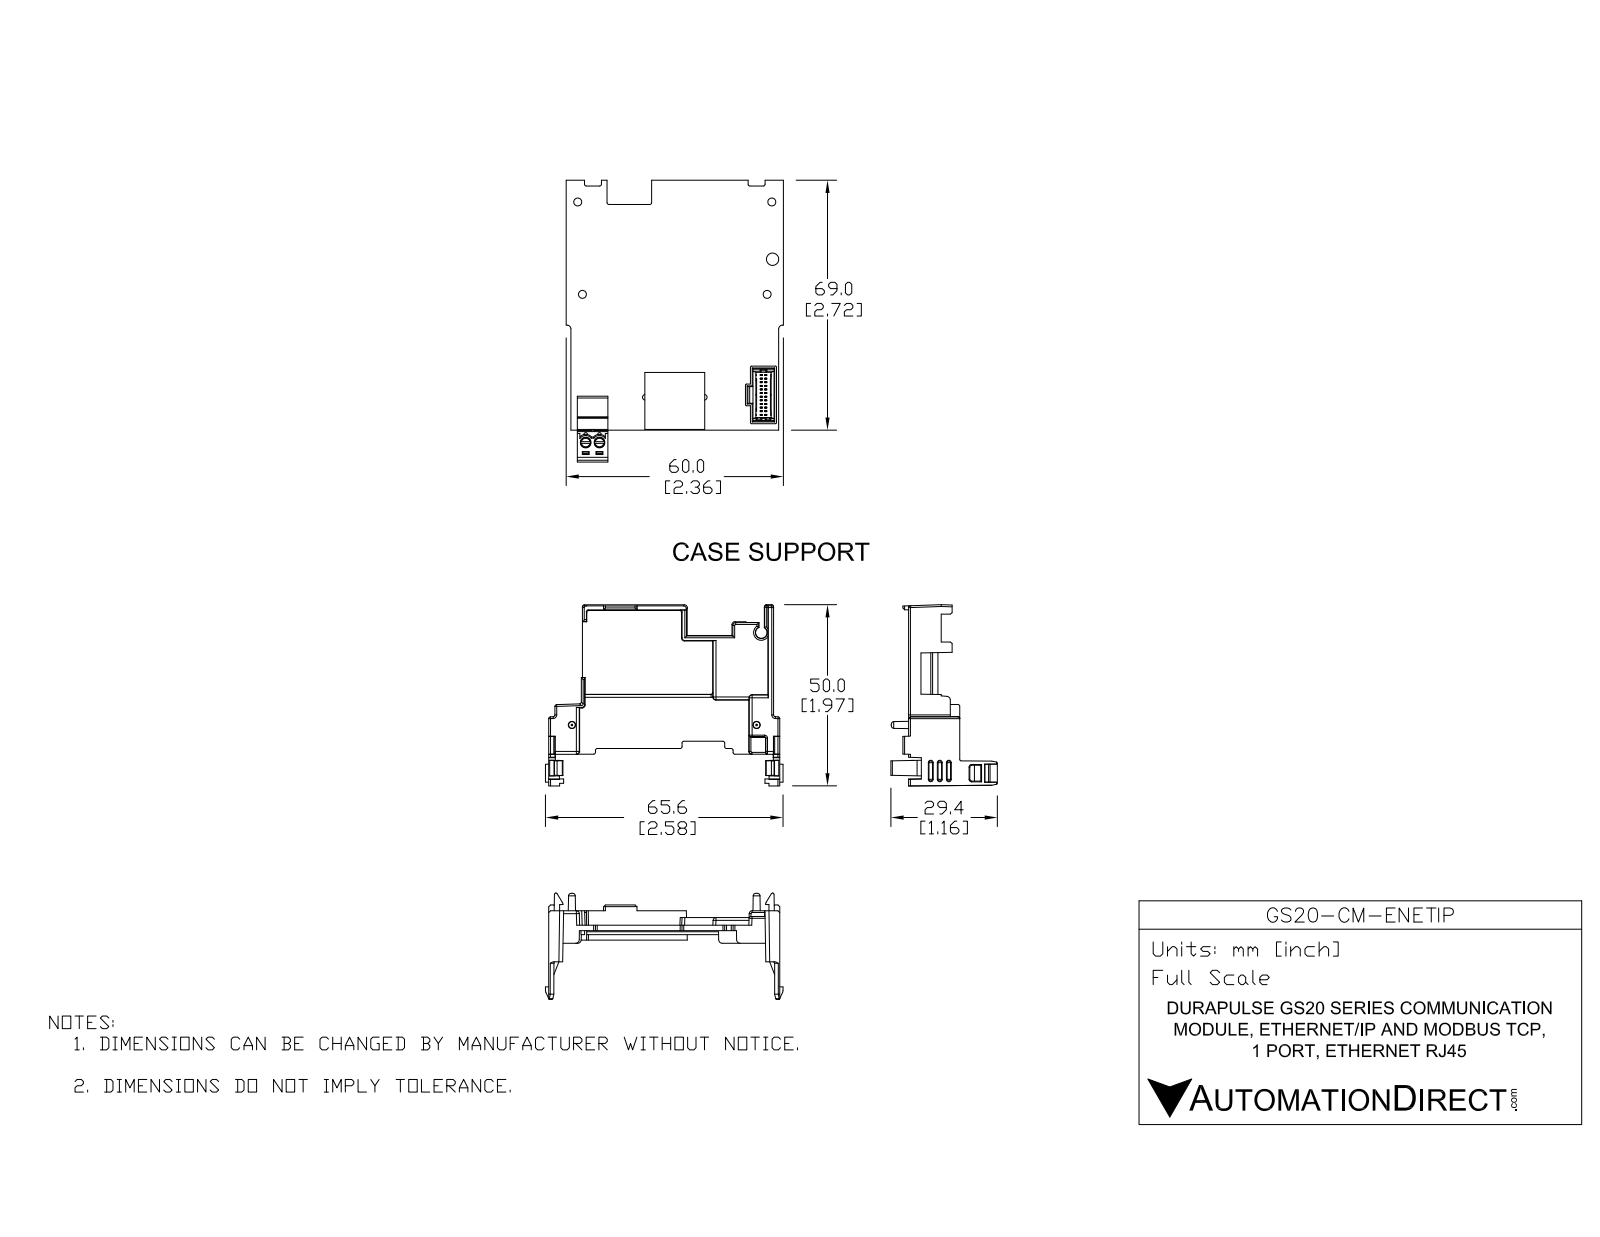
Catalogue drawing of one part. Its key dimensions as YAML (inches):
part_name: "GS20A-CM-ENETIP-3D00 fXT EXT 2 CUT Coord fXT"
step_written_by: "SolidWorks 2017 (AUTOMOTIVE_DESIGN)"
units: inches
bodies: {solids: 23, faces: 4743, planar: 3584, cylindrical: 1014, other: 145}
overall_size: [5.772, 2.583, 1.206]
volume: 1.436
surface_area: 47.02
round_holes:
  - {diameter: 0.087, count: 4}
  - {diameter: 0.045, count: 2}
  - {diameter: 0.106, count: 2}
  - {diameter: 0.114, count: 2}
  - {diameter: 0.157, count: 2}
  - {diameter: 0.134, count: 1}
round_bosses_or_shafts:
  - {diameter: 0.035, count: 8}
  - {diameter: 0.15, count: 2}
  - {diameter: 0.128, count: 2}
  - {diameter: 0.11, count: 2}
  - {diameter: 0.073, count: 2}
  - {diameter: 0.062, count: 2}
  - {diameter: 0.041, count: 2}
  - {diameter: 0.315, count: 1}
partial_cylinders:
  - {radius: 0.02, count: 98}
  - {radius: 0.004, count: 59}
  - {radius: 0.008, count: 40}
  - {radius: 0.012, count: 28}
  - {radius: 0.039, count: 27}
  - {radius: 0.031, count: 16}
  - {radius: 0.016, count: 13}
  - {radius: 0.006, count: 12}
face_to_face_distances: [0.063, 0.059, 0.043, 0.016, 0.26, 0.102, 0.157, 0.201, 0.264, 0.323]
hole_center_spacings: [0.025, 0.054, 0.15, 0.2, 1.005, 2.291, 0.022, 0.044]
